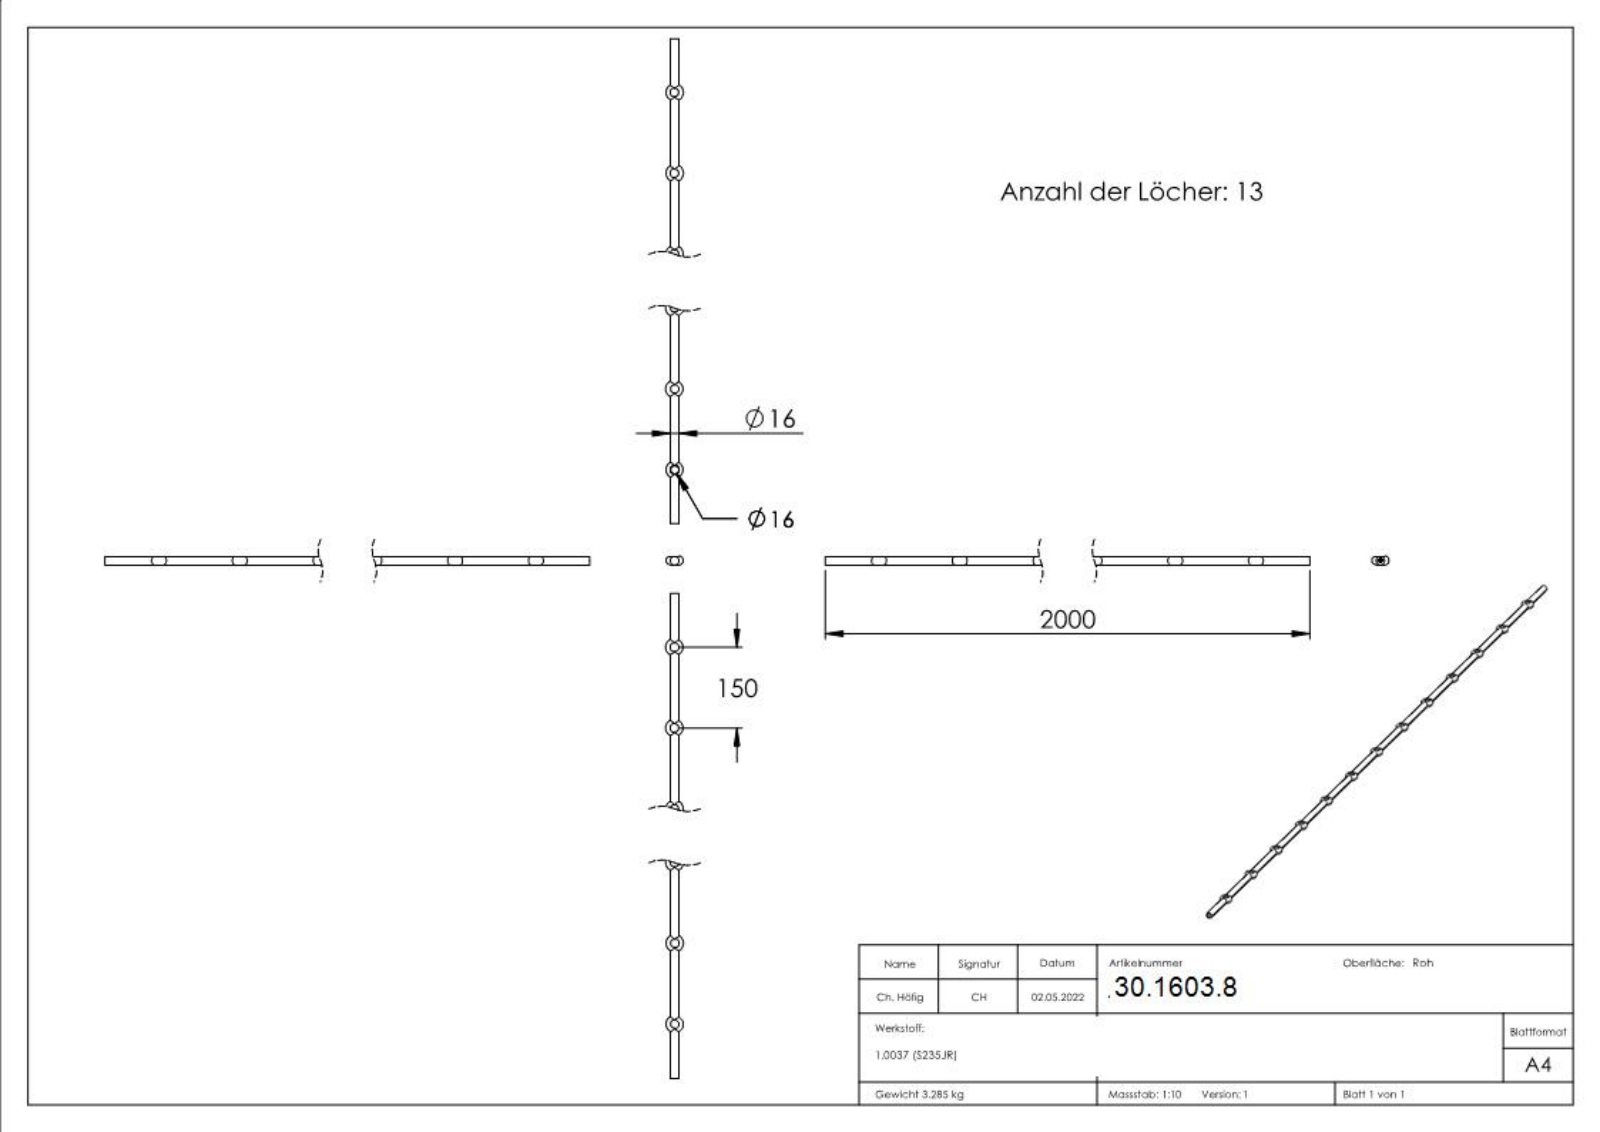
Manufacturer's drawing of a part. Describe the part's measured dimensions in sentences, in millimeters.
The part is named "42-2". Its 3-D file was written by "SolidWorks 2018 (CONFIG_CONTROL_DESIGN)". It is 1 solid with 257 faces: 124 planar, 27 cylindrical and 106 other. Overall it measures 2000 by 32 by 16 millimeters. Its volume is 421 236 cubic millimeters and its surface area 115 784 square millimeters. Round holes: 13 of diameter 16. Round bosses or shafts: 1 of diameter 16. The main face-to-face distances are 2000, 1999.9, 4.5, 1.14, 3.27, 0.34, 0.36, 2.9, 3.66, 1.96. The hole center spacings are 150, 300, 450, 600, 750, 900, 1050, 1200.
